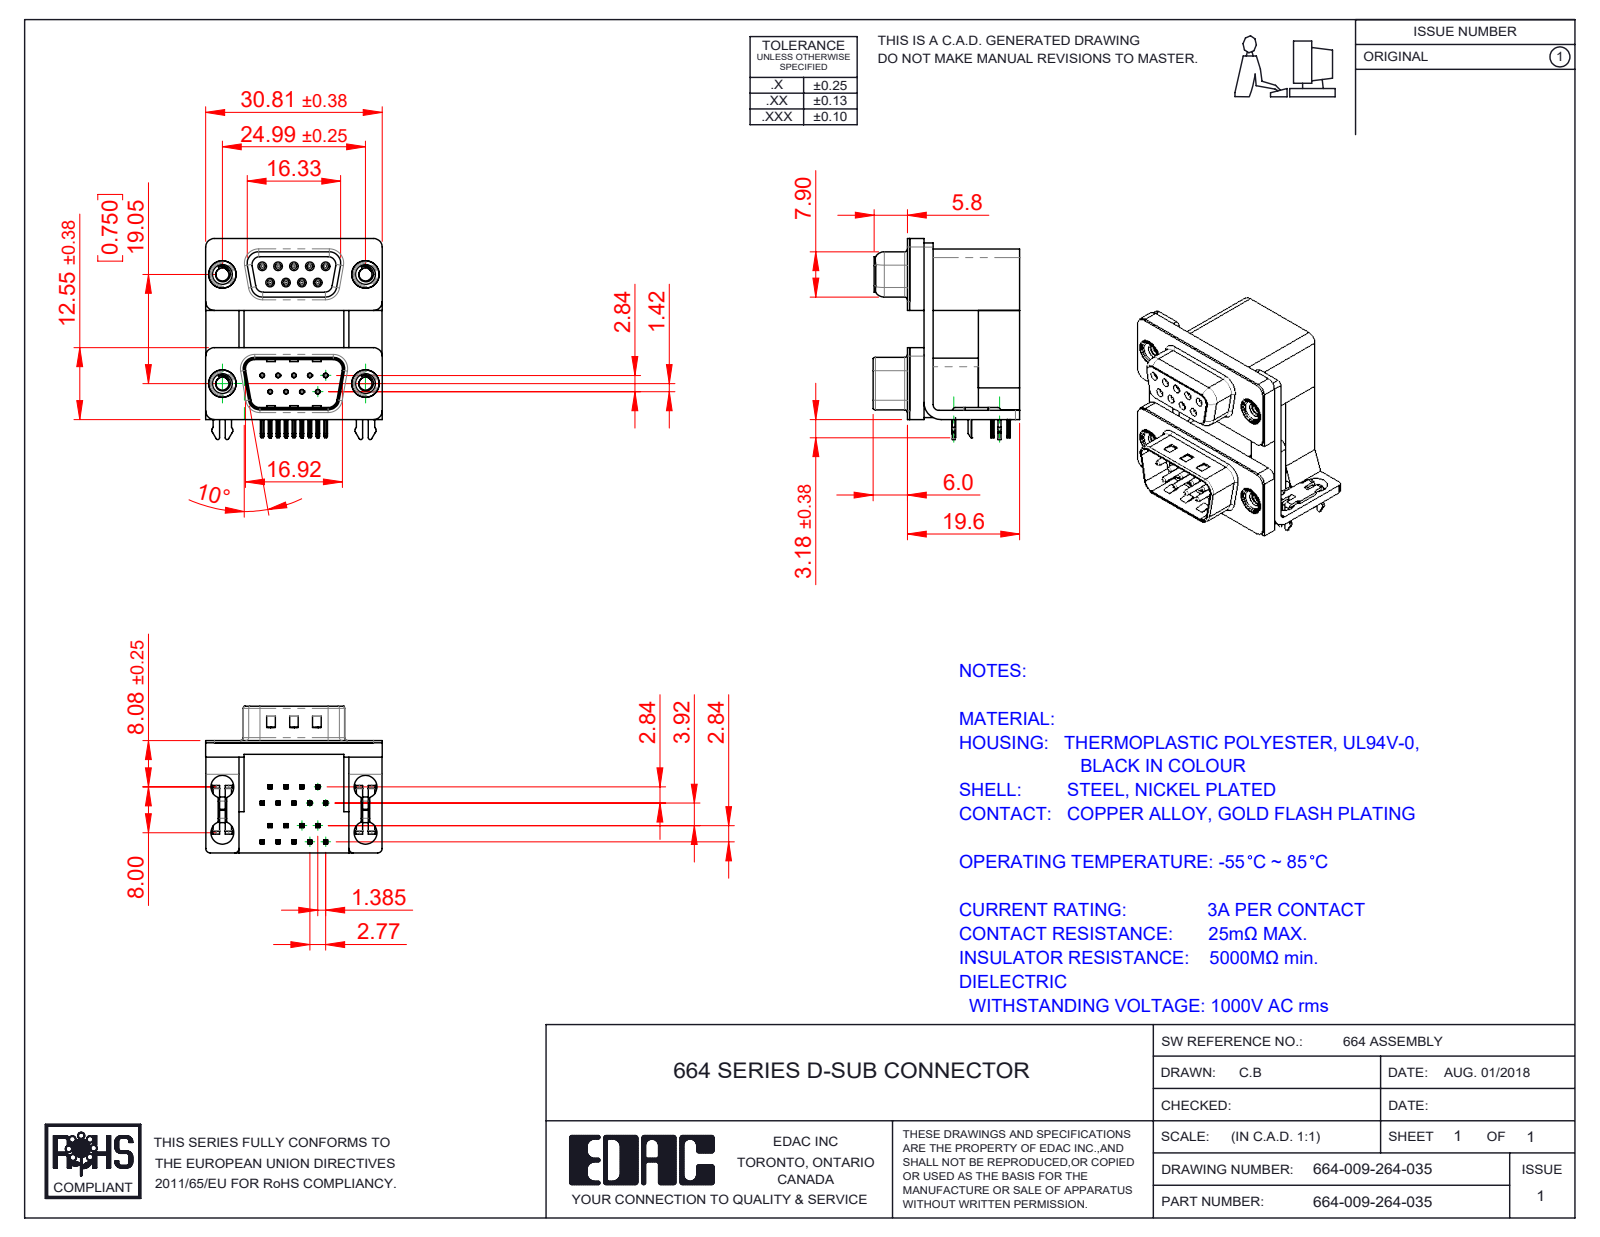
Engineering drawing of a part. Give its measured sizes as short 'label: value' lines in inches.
name: 664 Contact Top Upper_M; 664 Contact Bottom Lower; 664 Contact Bottom Upper_M; 664 Shell Receptacle_09 Contacts (+8 more)
written by: SolidWorks 2020 (CONFIG_CONTROL_DESIGN)
unit: in
bodies: 31 solids, 2681 faces (1365 planar, 745 cylindrical, 571 other)
size: 1.382 × 1.213 × 1.008
volume: 0.658 in³; area: 19.84 in²
holes: 18× ⌀0.031, 9× ⌀0.014, 9× ⌀0.035, 8× ⌀0.157, 4× ⌀0.089, 4× ⌀0.138, 4× ⌀0.189, 4× ⌀0.197
bosses: 9× ⌀0.047, 9× ⌀0.03, 4× ⌀0.193, 4× ⌀0.187, 4× ⌀0.154
rounds: 74× R0.004, 46× R0.01, 36× R0.006, 18× R0.005, 18× R0.014, 16× R0.02, 13× R0.059, 10× R0.03
face distances: 0.016, 0.098, 0.657, 0.756, 0.283, 0.374, 0.472, 0.063, 0.772, 0.488
hole spacings: 0.124, 0.109, 0.758, 0.75, 0.218, 0.781, 0.641, 0.863
